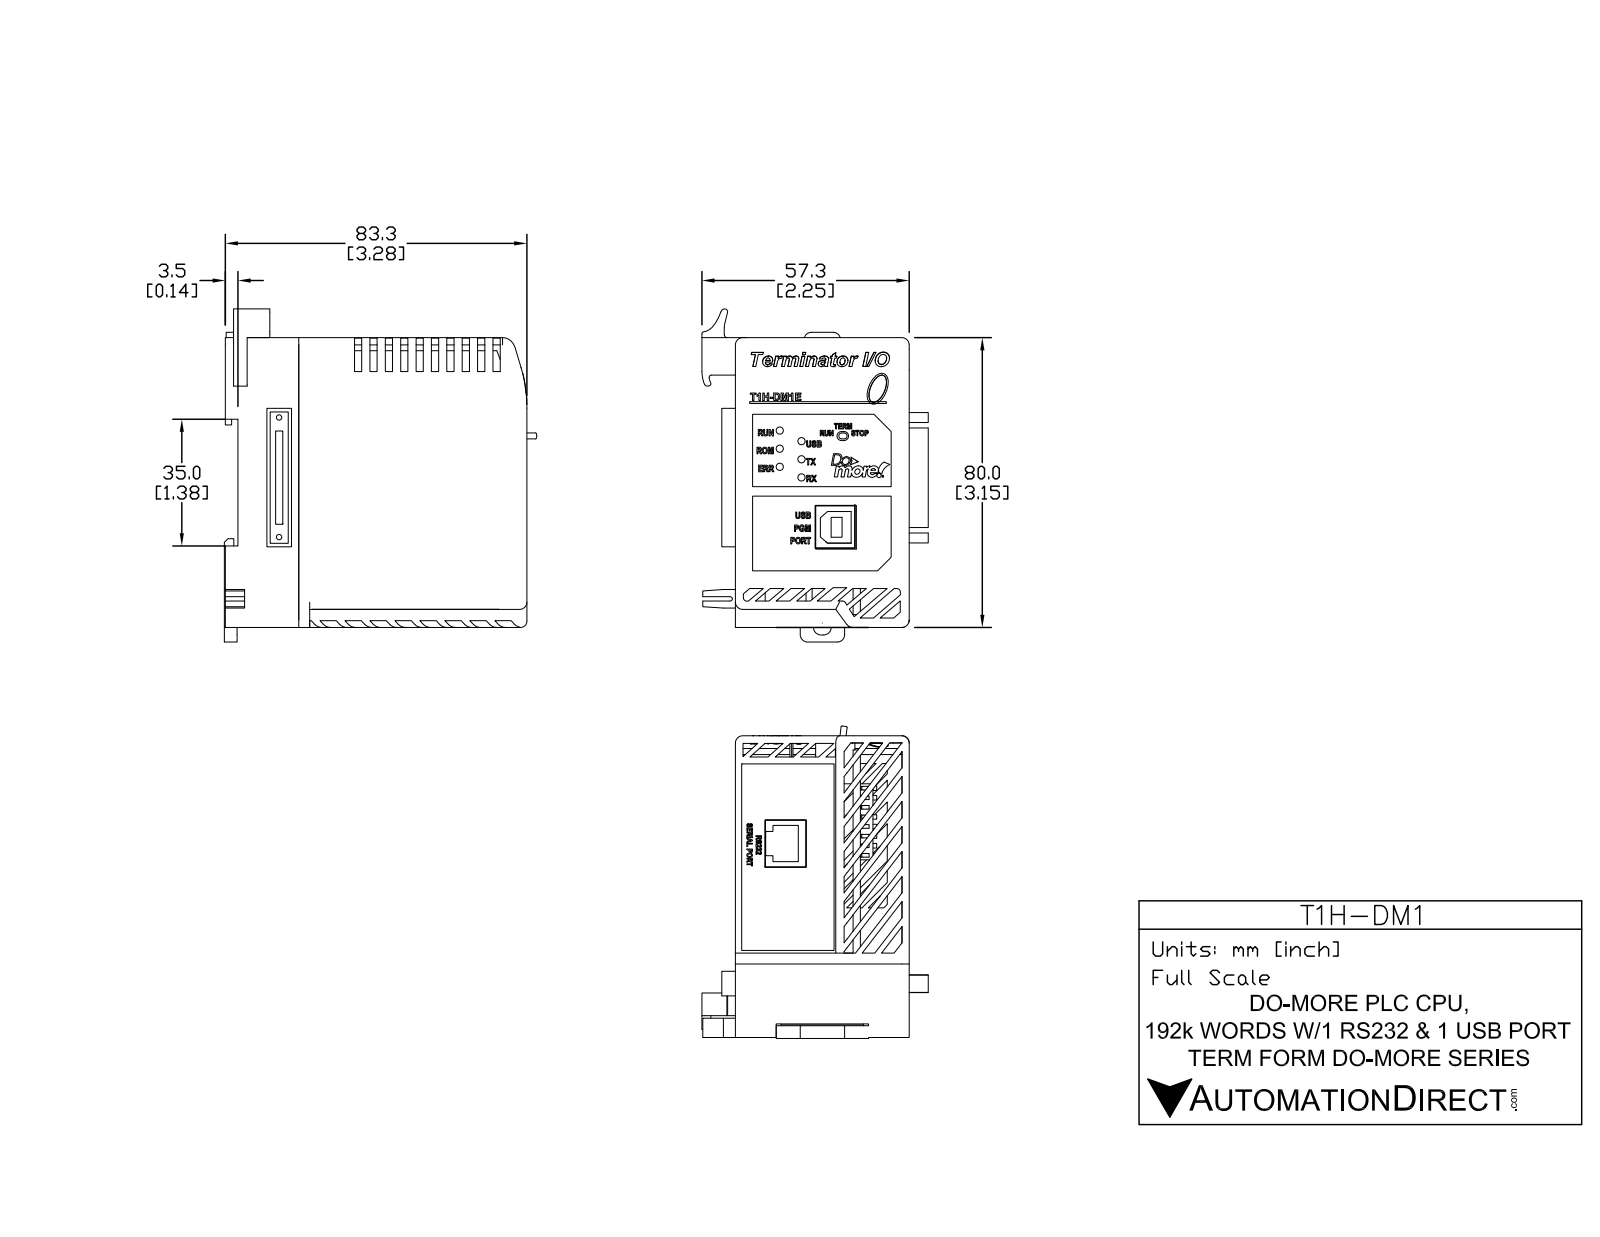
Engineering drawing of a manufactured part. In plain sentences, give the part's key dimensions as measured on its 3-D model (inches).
The part is named "T1H-DM1". Its 3-D file was written by "SolidWorks 2013 (AUTOMOTIVE_DESIGN)". It is 31 solids with 1893 faces: 1294 planar, 82 cylindrical and 517 other. Overall it measures 3.62 by 3.396 by 2.461 inches. Its volume is 6.397 cubic inches and its surface area 91 square inches. Round holes: 6 of diameter 0.079, 2 of diameter 0.079. Round bosses or shafts: 2 of diameter 0.059, 1 of diameter 0.065. Partial cylindrical surfaces (rounded edges, fillets, slot ends): 18 of radius 0.079, 12 of radius 0.039, 4 of radius 0.03, 2 of radius 0.049, 2 of radius 0.081, 1 of radius 0.033, 1 of radius 0.037, 1 of radius 0.06. The main face-to-face distances are 0.079, 1.811, 1.89, 1.732, 2.402, 0.138, 0.661, 3.063, 3.071, 2.874. The hole center spacings are 0.197, 0.263, 0.25, 0.391, 0.394, 0.365, 0.561, 1.309.
